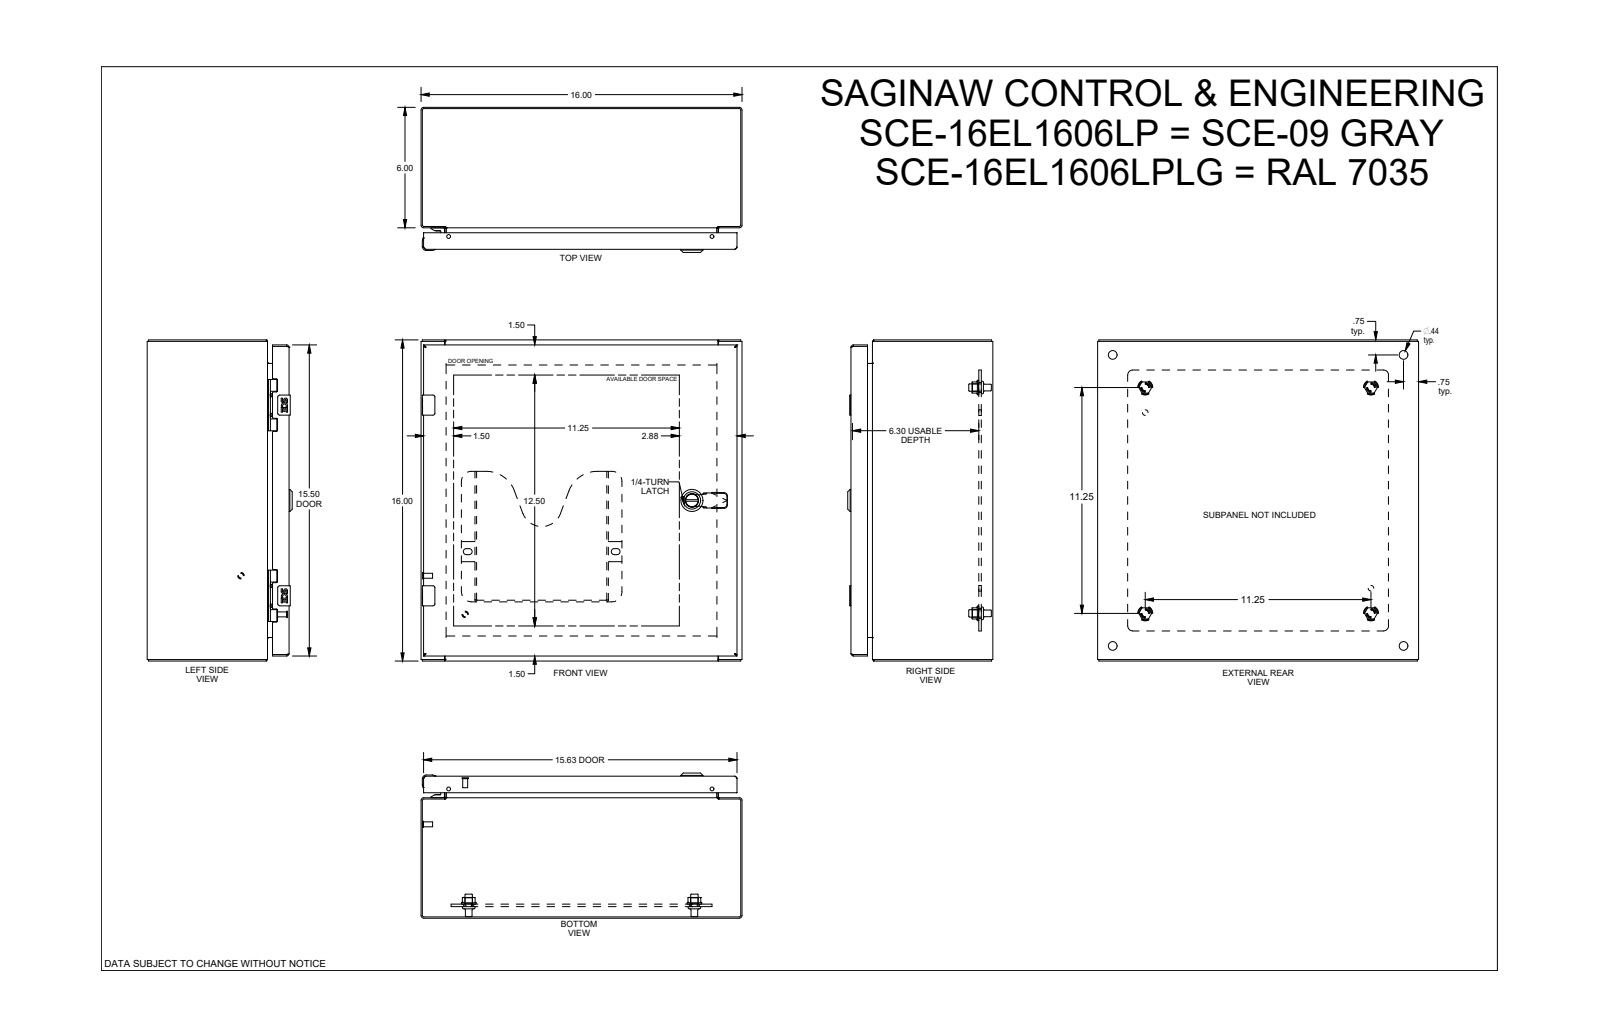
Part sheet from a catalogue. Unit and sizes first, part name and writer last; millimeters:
Units: millimetres
Overall size (bounding box): 406.4 × 406.4 × 183.6
Round holes (diameter × count): ⌀4.4 ×4, ⌀5.2 ×4, ⌀6.2 ×4, ⌀6.8 ×4, ⌀9.3 ×4, ⌀9.5 ×4, ⌀11.1 ×4, ⌀12.7 ×4, ⌀1 ×2, ⌀4 ×2, ⌀4.8 ×2, ⌀5.5 ×2
Round bosses / shafts (diameter × count): ⌀4.3 ×6, ⌀9.3 ×4, ⌀8.4 ×4, ⌀6.4 ×4, ⌀6.3 ×4, ⌀6.1 ×4, ⌀5 ×3, ⌀14.3 ×2
Partial cylindrical surfaces — rounded edges, fillets, slot ends (radius × count): R0.3 ×30, R0.3 ×28, R0.4 ×24, R1 ×17, R1.5 ×13, R0.5 ×12, R0.6 ×12, R0.7 ×12
Main face-to-face distances: 1.9, 1.5, 1.9, 179.7, 177.7, 178.1, 176.2, 404.5, 404.5, 406.4
Hole centre spacings: 241.3, 329.6, 25, 0.5, 12.5, 12.5, 58.4, 76
Volume: 1 819 000 mm³ · Surface area: 1 743 000 mm²
Bodies: 44 solids, 2355 faces (1039 planar, 618 cylindrical, 698 other)
Part name (STEP PRODUCT): SCE-16EL1606LP
STEP written by: SolidWorks 2019 (AUTOMOTIVE_DESIGN)
